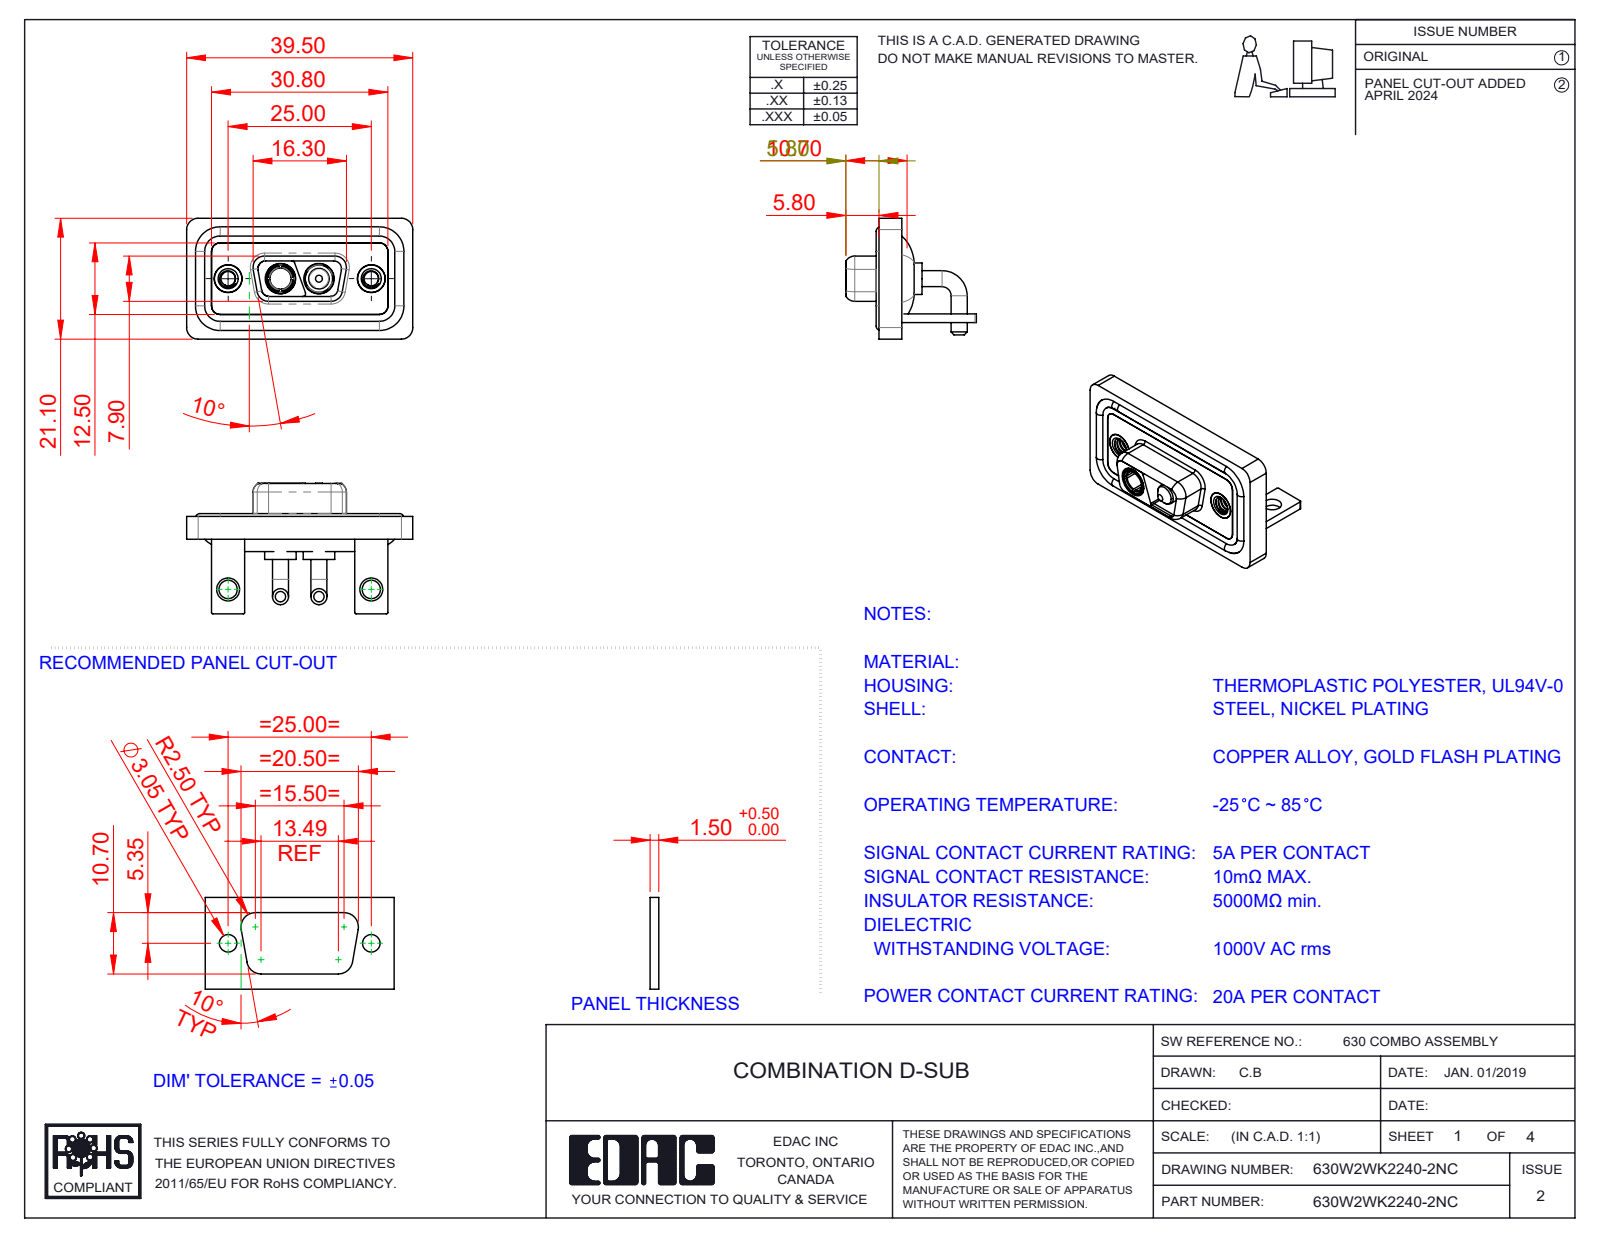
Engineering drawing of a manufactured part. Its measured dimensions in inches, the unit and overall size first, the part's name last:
Units: inches
Overall size (bounding box): 1.555 × 0.898 × 0.831
Round holes (diameter × count): ⌀0.191 ×4, ⌀0.098 ×2, ⌀0.126 ×2, ⌀0.157 ×2, ⌀0.159 ×2, ⌀0.197 ×2, ⌀0.209 ×2, ⌀0.146 ×1
Round bosses / shafts (diameter × count): ⌀0.11 ×4, ⌀0.063 ×4, ⌀0.217 ×2, ⌀0.205 ×2, ⌀0.195 ×2, ⌀0.189 ×2, ⌀0.187 ×2, ⌀0.148 ×2
Partial cylindrical surfaces — rounded edges, fillets, slot ends (radius × count): R0.079 ×19, R0.059 ×18, R0.01 ×16, R0.053 ×8, R0.063 ×8, R0.02 ×7, R0.024 ×4, R0.026 ×4
Main face-to-face distances: 0.016, 0.114, 0.059, 0.043, 0.146, 0.071, 0.031, 0.098, 0.063, 0.122
Hole centre spacings: 0.36, 0.624, 0.984, 0.265
Volume: 0.309 in³ · Surface area: 12.76 in²
Bodies: 13 solids, 550 faces (164 planar, 257 cylindrical, 129 other)
Part name (STEP PRODUCT): Power Socket_20A RA; Power Pin_20A RA; 630Combo Stabilizer Bracket_50 Contacts; 630W2WK2140-2NC (+5 more)
STEP written by: SolidWorks 2023 (CONFIG_CONTROL_DESIGN)
